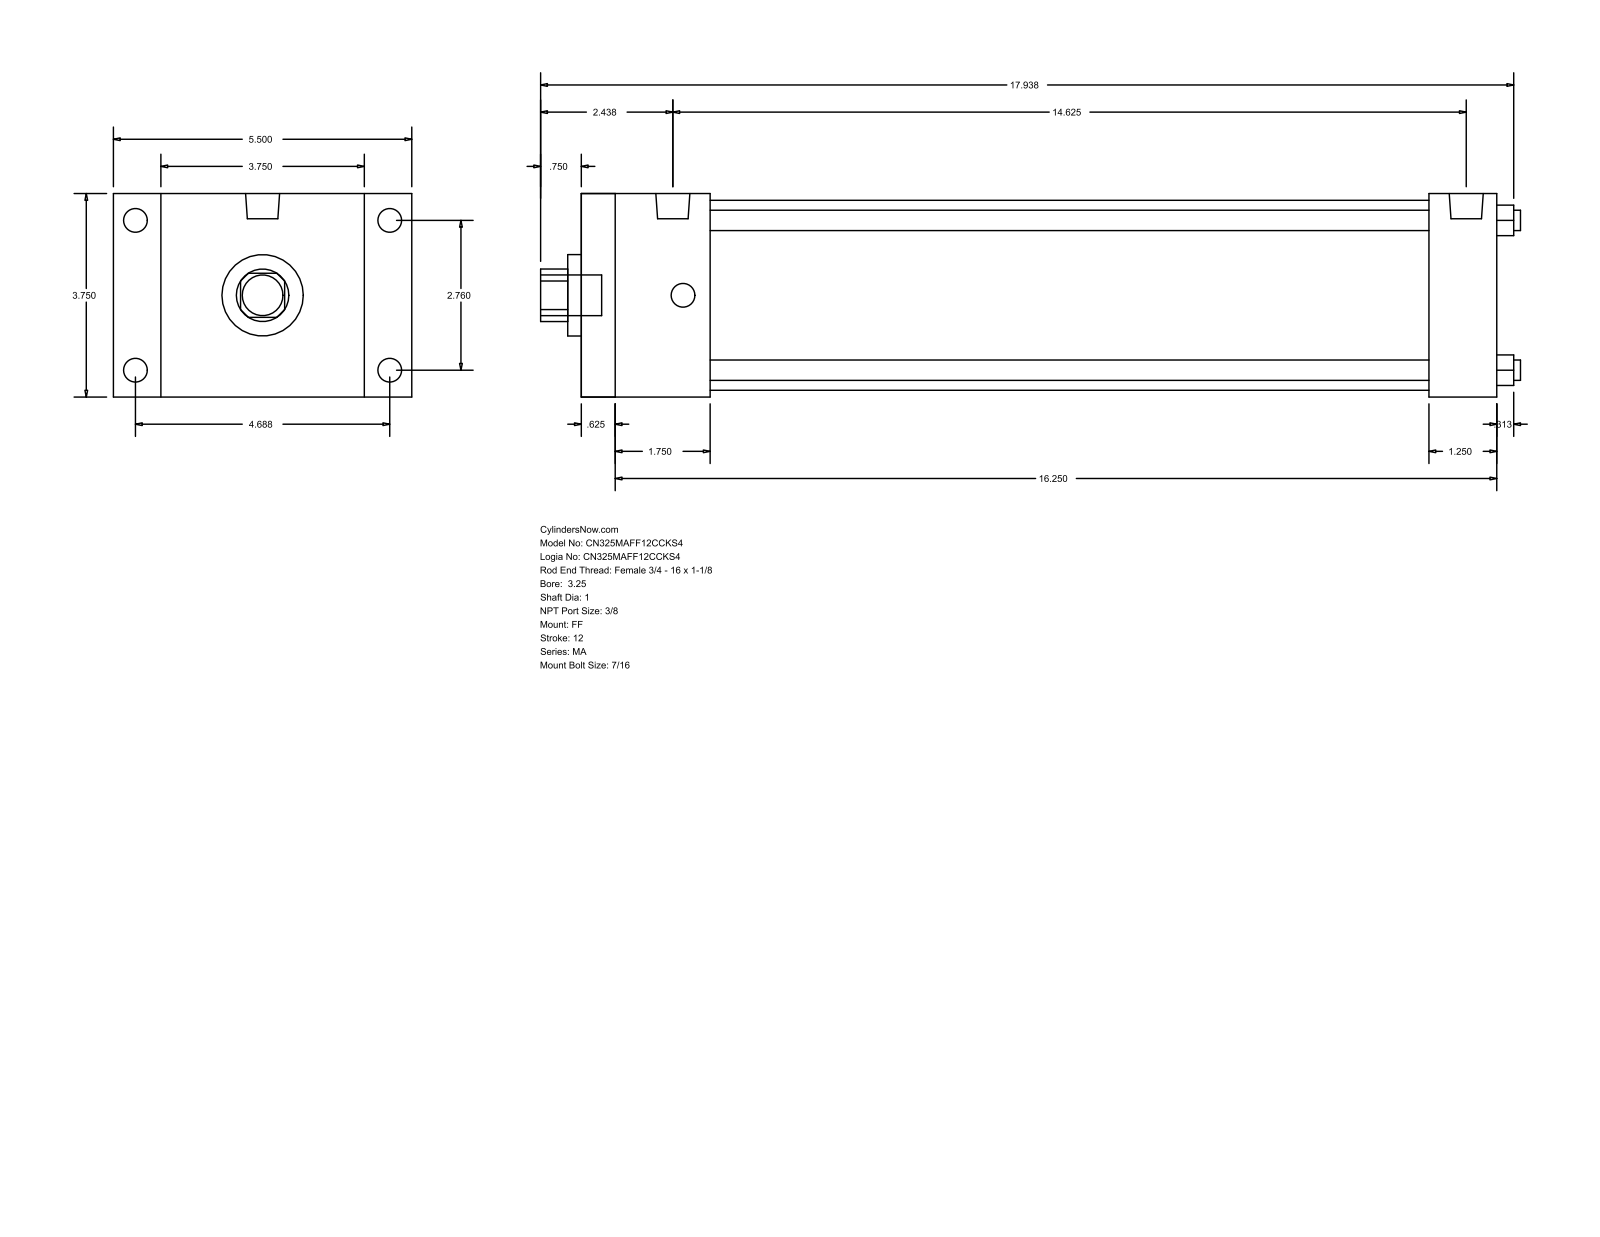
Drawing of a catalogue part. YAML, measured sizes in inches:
part_name: "MA_FF__0325_1"
step_written_by: "GSSL Pune (CONFIG_CONTROL_DESIGN)"
units: inches
bodies: {solids: 0, faces: 92, planar: 64, cylindrical: 28, other: 0}
overall_size: [18.063, 5.5, 3.75]
round_holes:
  - {diameter: 0.375, count: 4}
  - {diameter: 1, count: 1}
  - {diameter: 1.5, count: 1}
  - {diameter: 3.5, count: 1}
round_bosses_or_shafts:
  - {diameter: 0.437, count: 8}
  - {diameter: 0.627, count: 2}
  - {diameter: 0.75, count: 1}
partial_cylinders:
  - {radius: 0.484, count: 1}
face_to_face_distances: [3.75, 16.875, 0.625, 16.25, 0.875, 4.625, 2.375, 15.625, 1.75, 15]
hole_center_spacings: [1.952, 2.76, 3.903]
